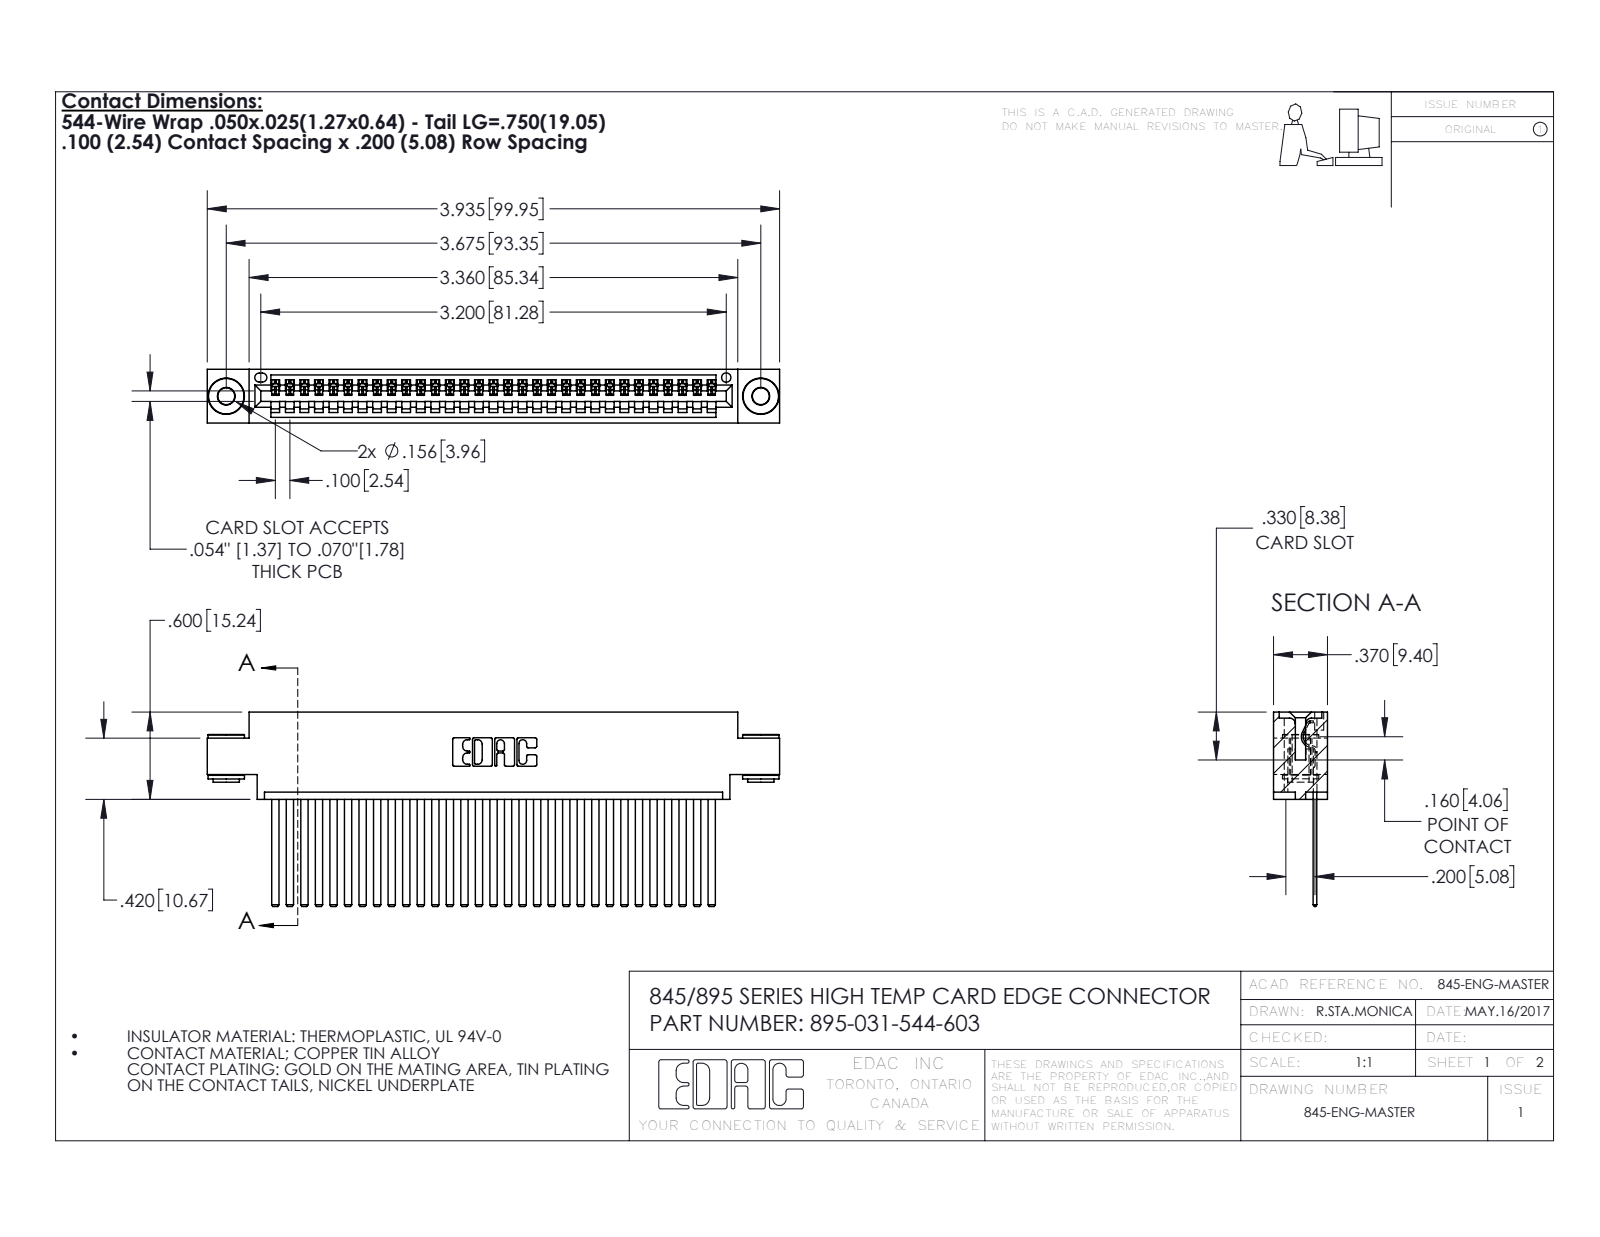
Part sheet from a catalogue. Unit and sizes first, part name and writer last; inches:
Units: inches
Overall size (bounding box): 3.935 × 1.337 × 0.37
Round holes (diameter × count): ⌀0.116 ×2, ⌀0.156 ×2, ⌀0.064 ×1
Round bosses / shafts (diameter × count): ⌀0.25 ×2, ⌀0.18 ×2, ⌀0.136 ×2
Partial cylindrical surfaces — rounded edges, fillets, slot ends (radius × count): R0.006 ×62, R0.01 ×22, R0.007 ×6, R0.031 ×6, R0.026 ×3, R0.031 ×2, R0.04 ×2, R0.014 ×1
Main face-to-face distances: 0.072, 0.298, 0.025, 0.098, 0.272, 0.37, 0.2, 0.225, 0.175, 0.149
Hole centre spacings: 0.27, 3.44, 3.675
Volume: 0.59 in³ · Surface area: 21.88 in²
Bodies: 34 solids, 1780 faces (1210 planar, 562 cylindrical, 8 other)
Part name (STEP PRODUCT): 345 Part_0.170 Offset - 0.156 Dia-TH; 345-250-002_345-250-002-102; 345-292-001_345-293-144; 395-031-544-603
STEP written by: SolidWorks 2016 (CONFIG_CONTROL_DESIGN)
